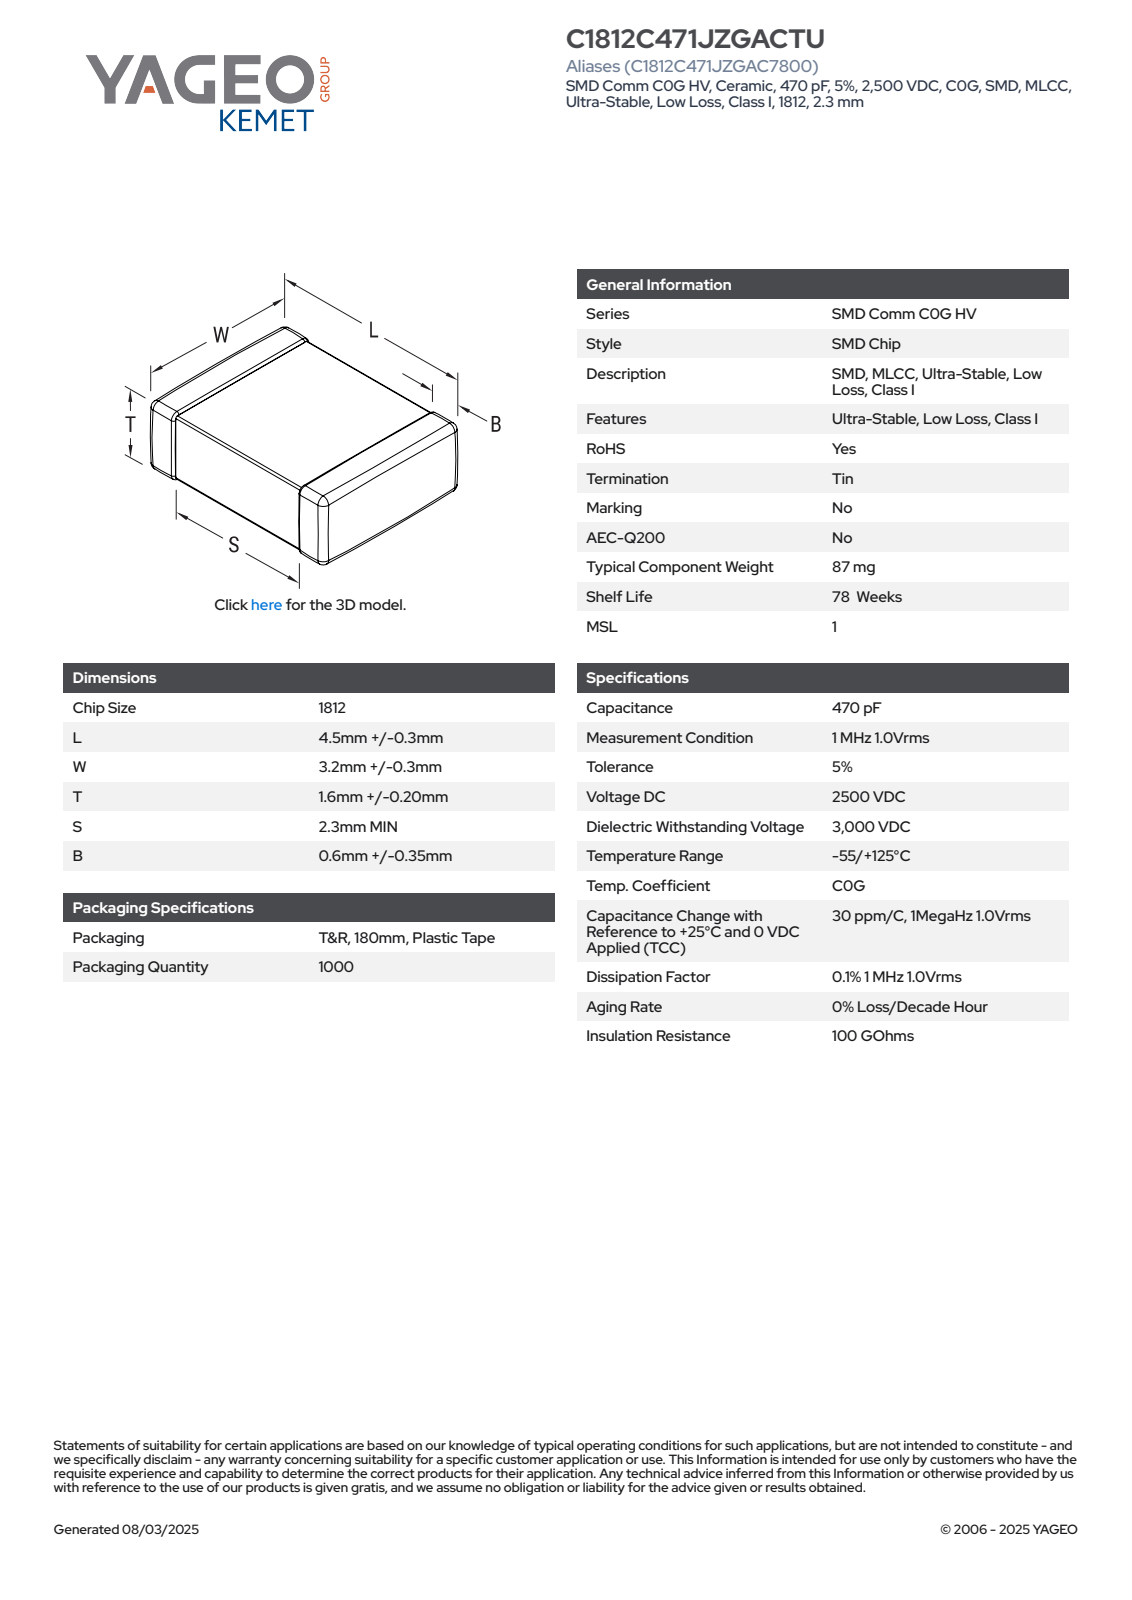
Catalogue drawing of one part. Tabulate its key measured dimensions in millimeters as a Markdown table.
| quantity | value |
| --- | --- |
| part name | CCS_CCSTDNOS_1812_L4.8W3.5T1.8B0.95 |
| STEP written by | SolidWorks 2014 (AUTOMOTIVE_DESIGN) |
| units | millimeters |
| bodies | 4 solids, 125 faces (71 planar, 38 cylindrical, 16 other) |
| overall size | 4.8 × 3.5 × 1.8 |
| volume | 28 mm³ |
| surface area | 62 mm² |
| main face-to-face distances | 1.73, 1.66, 4.8, 1.8, 3.43, 3.36, 3.5, 1.49, 0.34, 1.94 |
